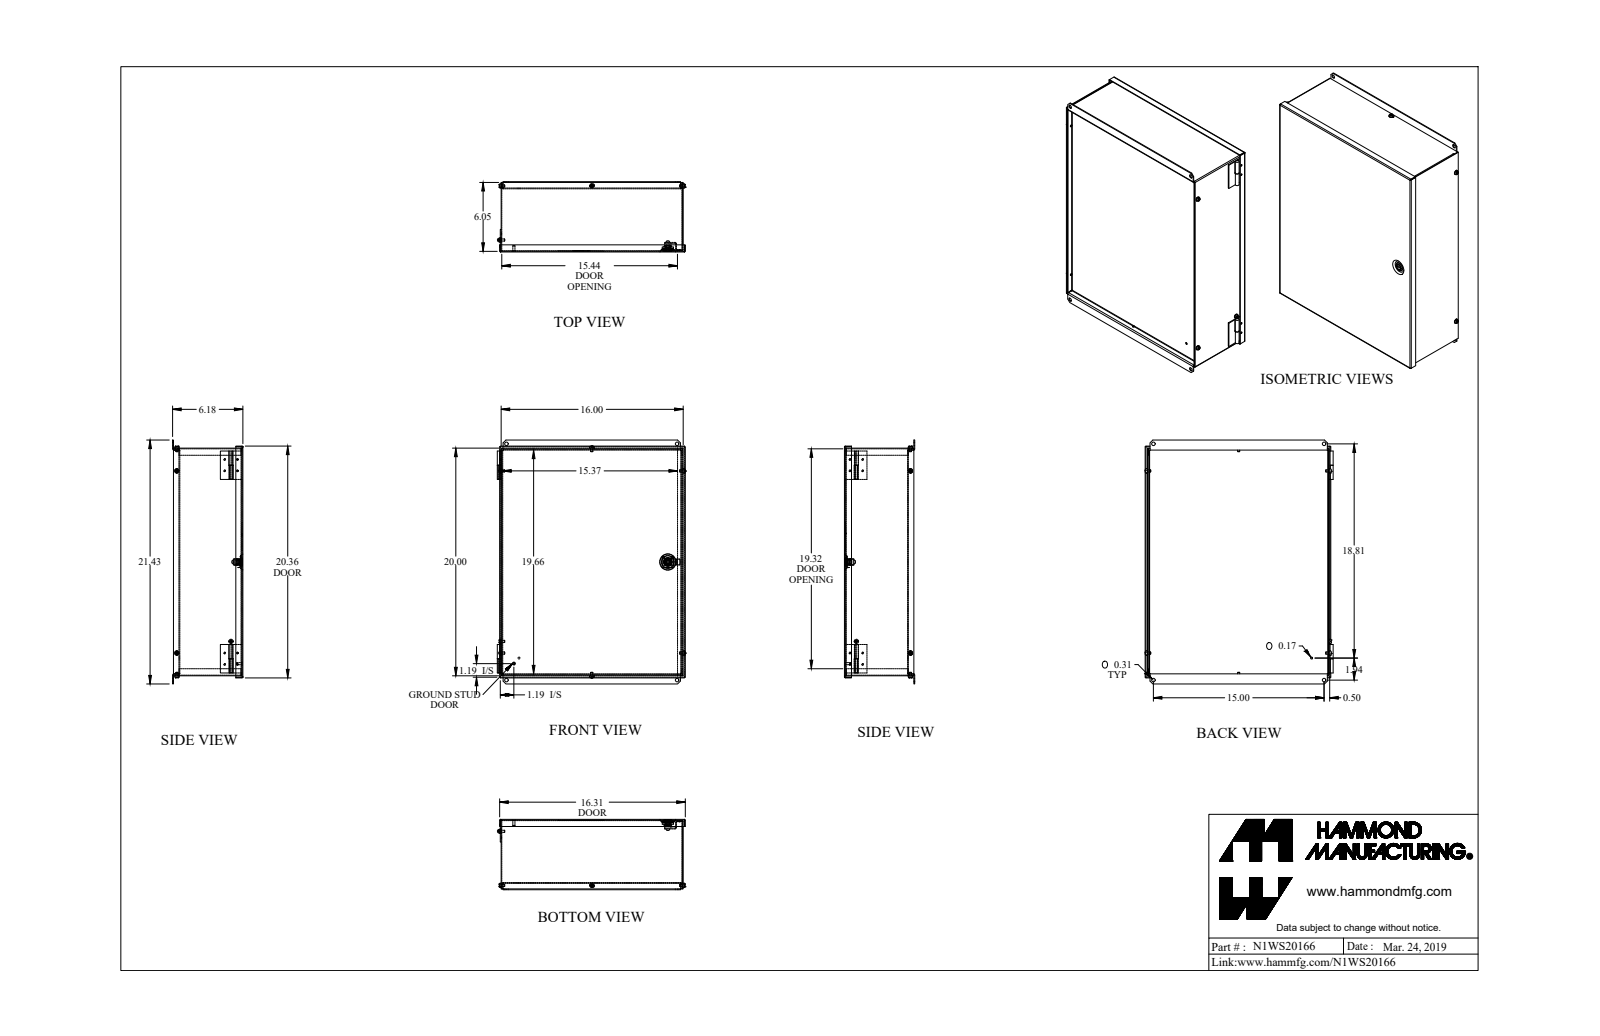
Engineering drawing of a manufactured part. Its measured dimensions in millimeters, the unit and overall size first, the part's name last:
Units: millimetres
Overall size (bounding box): 544.2 × 419.6 × 156.9
Round holes (diameter × count): ⌀3.6 ×8, ⌀4.3 ×5, ⌀7.9 ×4, ⌀4.7 ×1, ⌀8.1 ×1, ⌀12.1 ×1
Round bosses / shafts (diameter × count): ⌀3.3 ×8, ⌀4.8 ×4, ⌀9.5 ×3, ⌀20 ×1, ⌀13.9 ×1, ⌀12 ×1, ⌀11.9 ×1, ⌀9.5 ×1
Partial cylindrical surfaces — rounded edges, fillets, slot ends (radius × count): R0.7 ×9, R2.2 ×9, R0.9 ×8, R2.7 ×6, R2.8 ×6, R0.3 ×4, R2.5 ×4, R2 ×2
Main face-to-face distances: 1.4, 1.8, 1.4, 141.3, 142.8, 139.5, 140.9, 405, 506.6, 403.5
Hole centre spacings: 25.4, 28.4, 38.1, 431.8, 432.7, 406.4, 106.6, 109.6
Volume: 1 224 000 mm³ · Surface area: 1 570 000 mm²
Bodies: 17 solids, 607 faces (328 planar, 214 cylindrical, 65 other)
Part name (STEP PRODUCT): N1WS20166
STEP written by: SolidWorks 2018 (AUTOMOTIVE_DESIGN)
